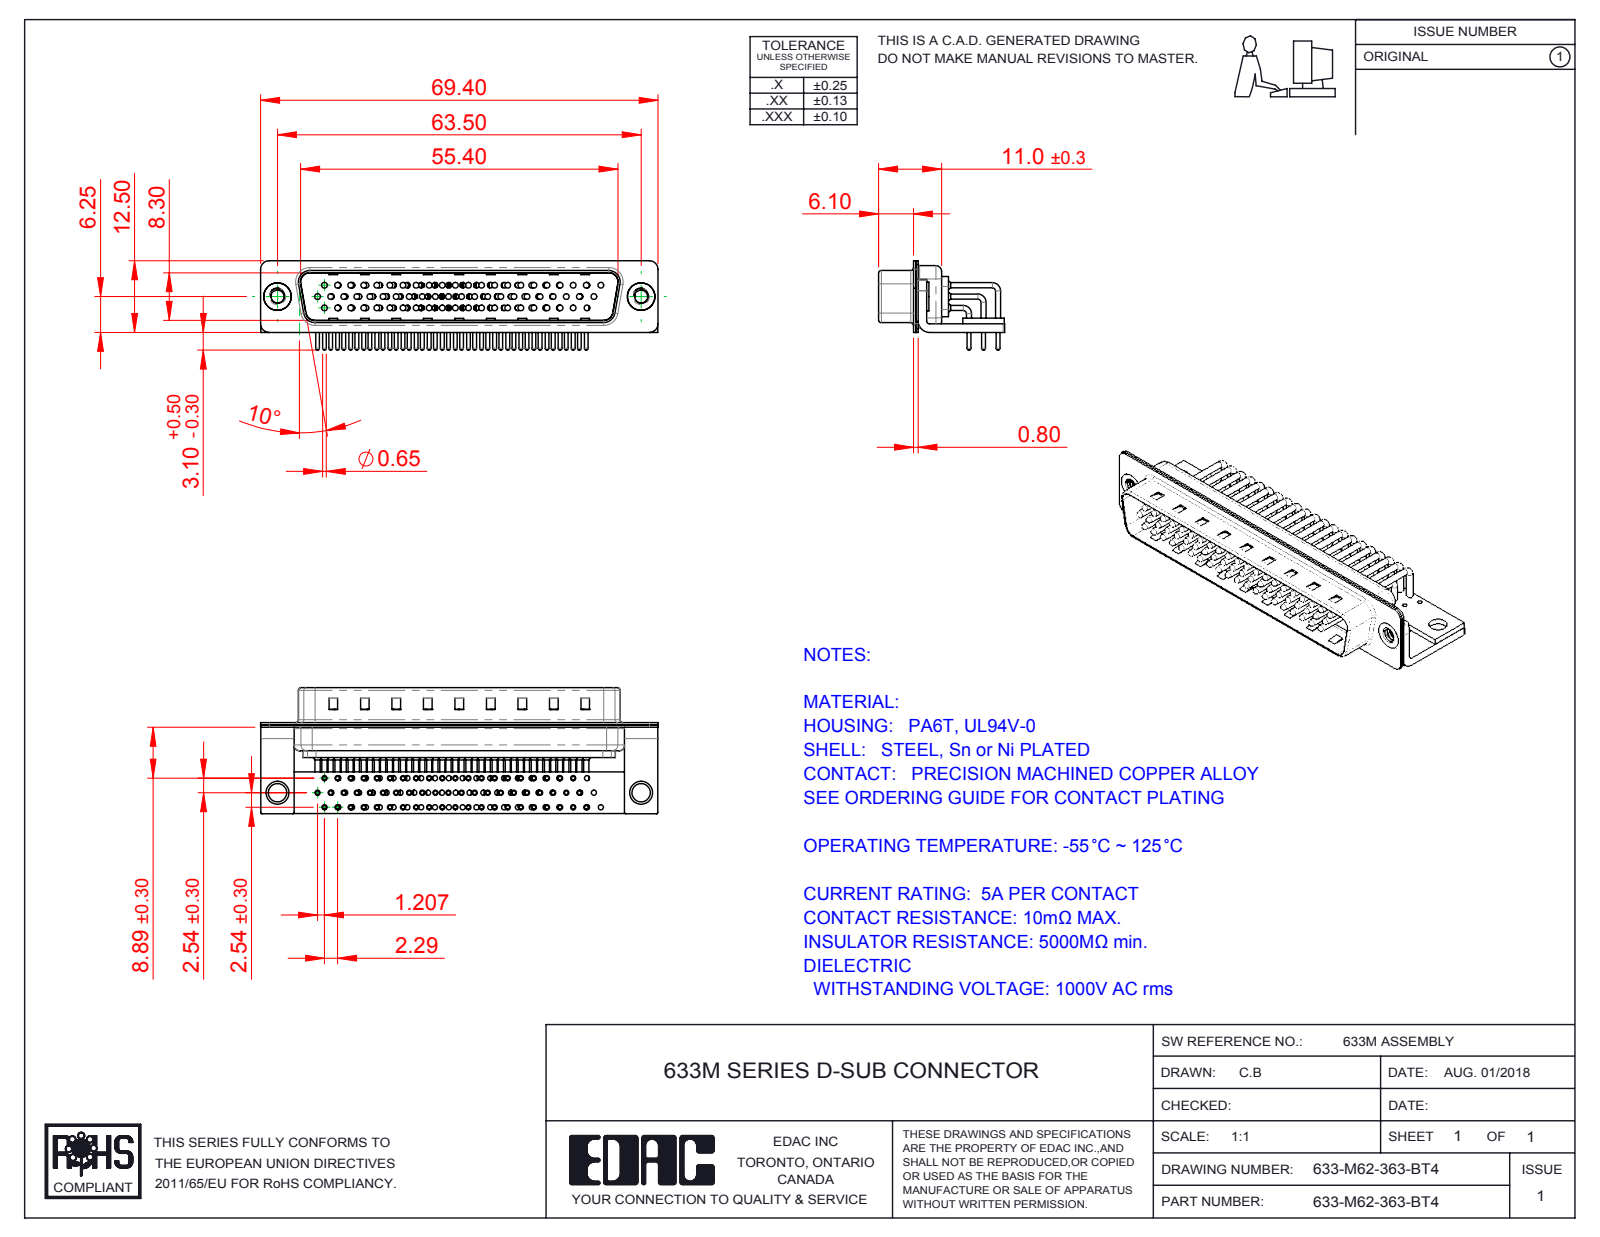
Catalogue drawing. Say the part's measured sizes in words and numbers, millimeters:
The part is named "633M Contact Row 3; 633M Contact Row 1; 633M Housing_62 Contacts; 633M 4-40 Threaded Rivet_Stabilizer (+6 more)". Its 3-D file was written by "SolidWorks 2016 (CONFIG_CONTROL_DESIGN)". It is 70 solids with 7406 faces: 4197 planar, 2519 cylindrical and 690 other. Overall it measures 69.4 by 22 by 15.6 millimeters. Its volume is 5 073 cubic millimeters and its surface area 15 493 square millimeters. Round holes: 62 of diameter 0.9, 62 of diameter 1, 62 of diameter 1.7, 62 of diameter 2, 2 of diameter 2.26, 2 of diameter 3.2, 2 of diameter 4, 2 of diameter 4.8. Round bosses or shafts: 118 of diameter 0.9, 62 of diameter 1.5, 62 of diameter 0.65, 56 of diameter 1, 2 of diameter 5, 2 of diameter 4.9. Partial cylindrical surfaces (rounded edges, fillets, slot ends): 62 of radius 1.01, 16 of radius 0.25, 16 of radius 1.5, 13 of radius 2, 9 of radius 0.5, 8 of radius 1.6, 4 of radius 0.6, 4 of radius 0.65. The main face-to-face distances are 0.4, 0.85, 1.25, 1.5, 9.55, 1, 1.9, 10.4, 0.8, 8.3. The hole center spacings are 7.24, 2.41, 9.65, 4.83, 14.48, 16.89, 2.81, 2.32.
